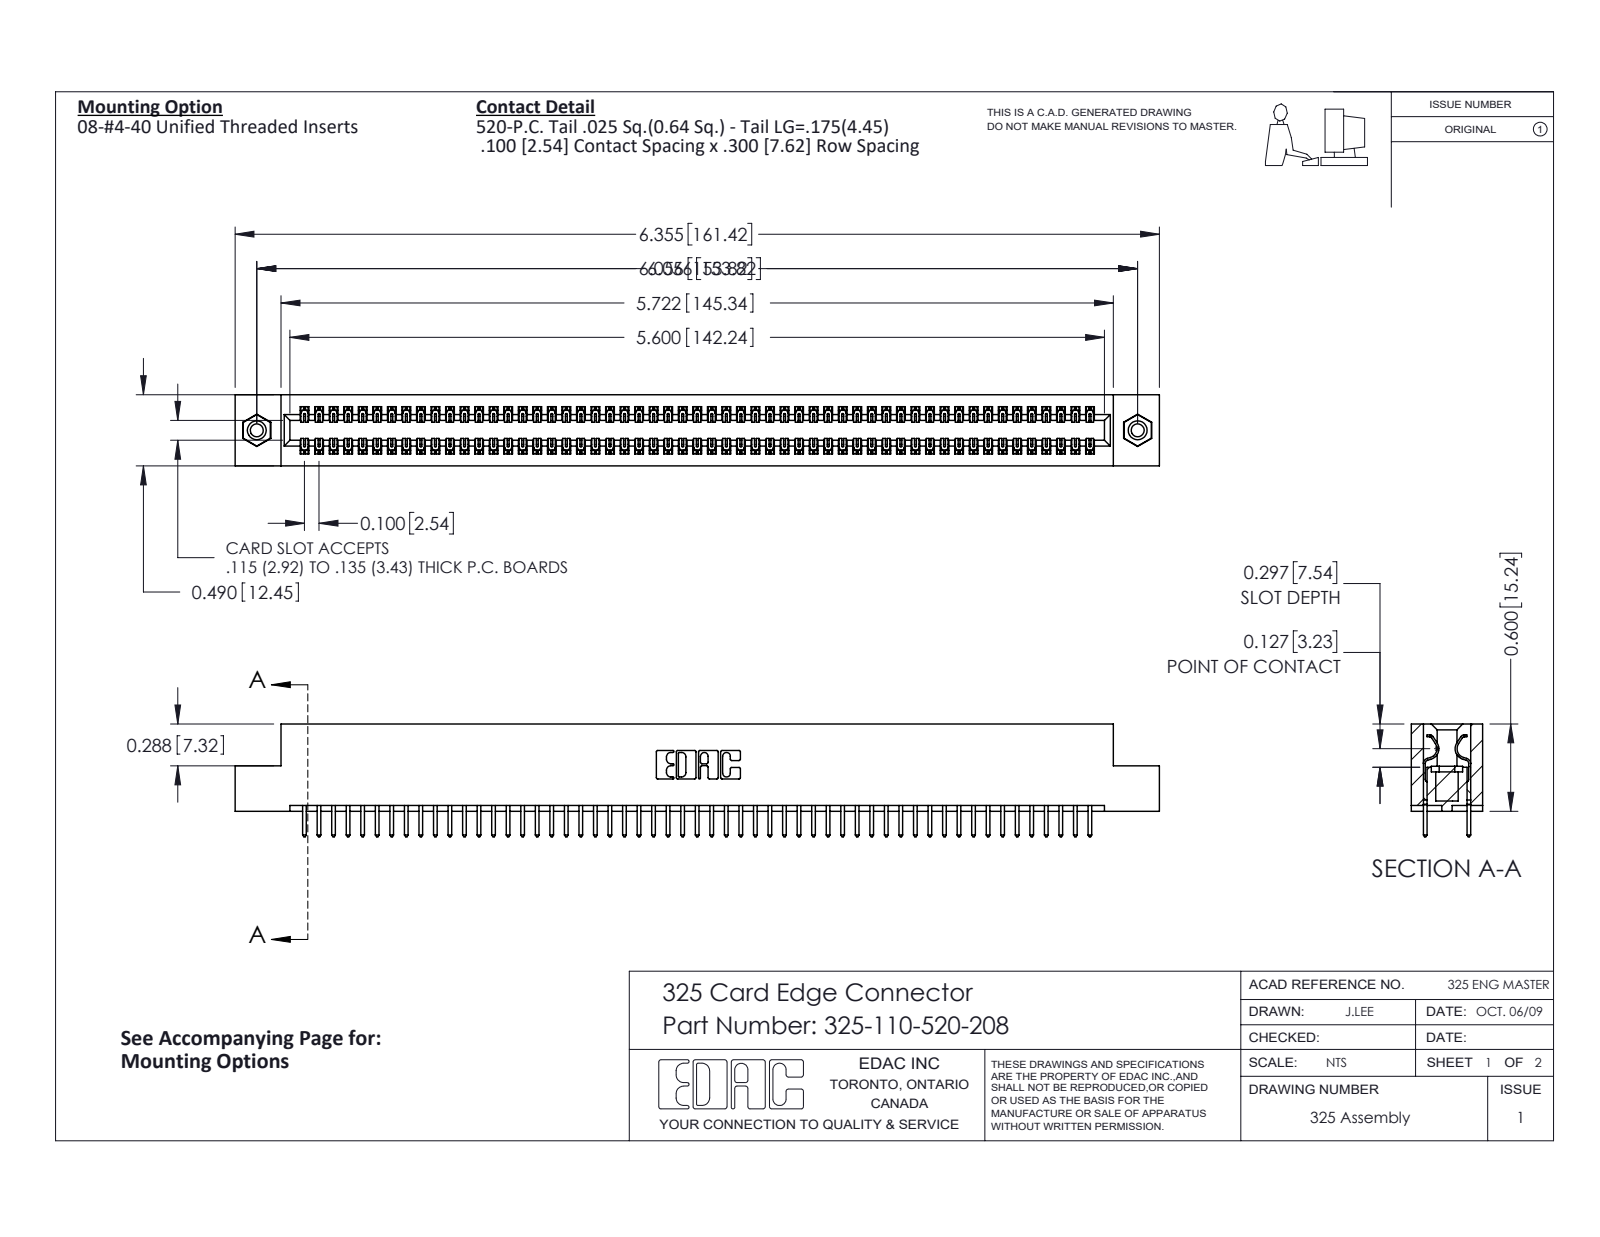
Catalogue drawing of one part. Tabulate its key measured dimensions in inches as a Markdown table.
| quantity | value |
| --- | --- |
| part name | 325-110-520-208; 345-250-001_345-250-003-102; 325-292-001_325-293-120; 325 Part_TI |
| STEP written by | SolidWorks 2016 (CONFIG_CONTROL_DESIGN) |
| units | inches |
| bodies | 113 solids, 5894 faces (4062 planar, 1816 cylindrical, 16 other) |
| overall size | 6.355 × 0.775 × 0.49 |
| volume | 1.277 in³ |
| surface area | 39.42 in² |
| round holes (diameter × count) | 0.089 × 2, 0.125 × 2, 0.16 × 2 |
| round bosses / shafts (diameter × count) | 0.155 × 2 |
| partial cylindrical surfaces (radius × count) | 0.006 × 165, 0.01 × 110, 0.01 × 22, 0.007 × 6, 0.031 × 6, 0.026 × 3, 0.014 × 2, 0.022 × 2 |
| main face-to-face distances | 0.083, 0.407, 0.49, 0.3, 0.107, 0.383, 0.025, 0.325, 0.275, 0.263 |
| hole center spacings | 6.056 |
